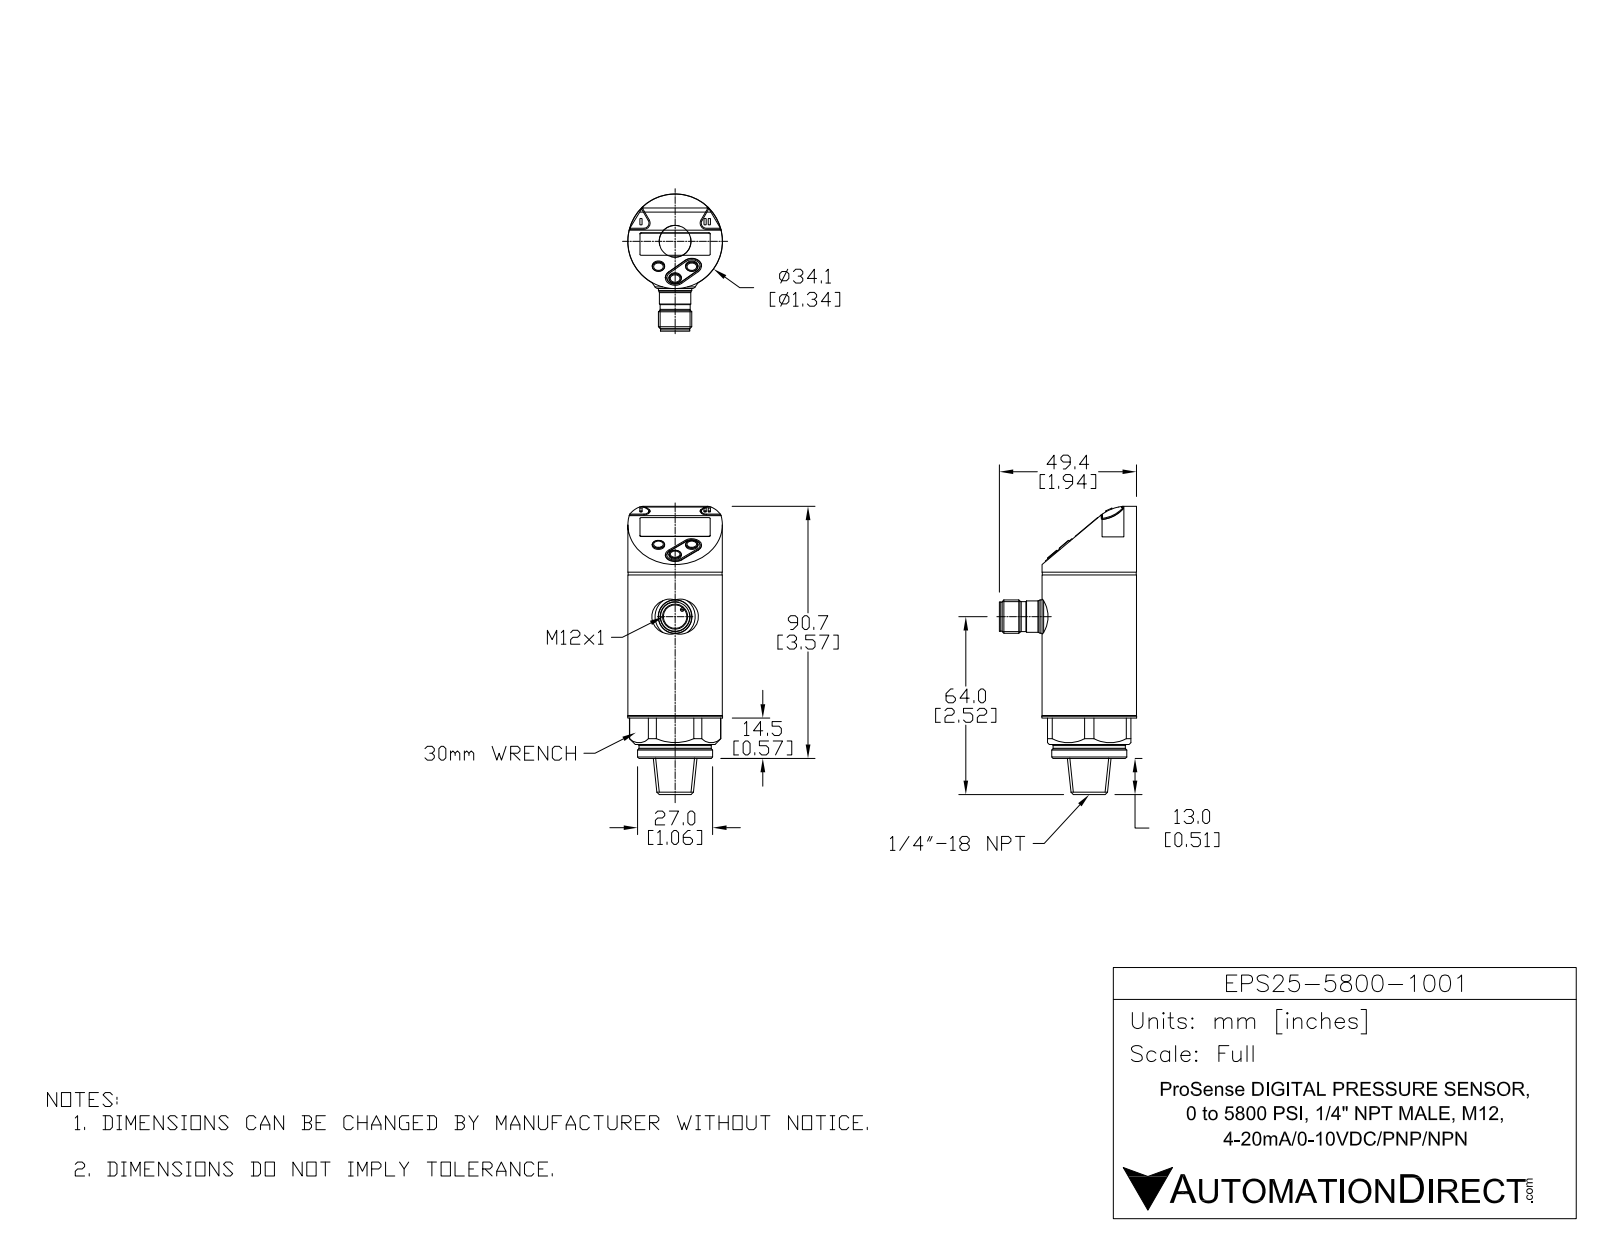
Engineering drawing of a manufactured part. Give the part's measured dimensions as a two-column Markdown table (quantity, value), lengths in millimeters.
| quantity | value |
| --- | --- |
| part name | EPS25-5800-1001 |
| STEP written by | SolidWorks 2016 (AUTOMOTIVE_DESIGN) |
| units | millimeters |
| bodies | 11 solids, 370 faces (207 planar, 84 cylindrical, 79 other) |
| overall size | 103.7 × 49.4 × 34.1 |
| volume | 72 203 mm³ |
| surface area | 21 365 mm² |
| round holes (diameter × count) | 4.2 × 1, 8.45 × 1 |
| round bosses / shafts (diameter × count) | 1.4 × 4, 1 × 4, 34.1 × 1, 34 × 1, 33.8 × 1, 27 × 1, 26 × 1, 12 × 1 |
| partial cylindrical surfaces (radius × count) | 1.8 × 2, 2.2 × 2, 3 × 2, 3.5 × 2, 15 × 2, 0.61 × 1, 6.8 × 1, 16.44 × 1 |
| main face-to-face distances | 0.68, 11.5, 12.18, 10.68, 1.5, 10, 2, 2.5, 14, 4 |
